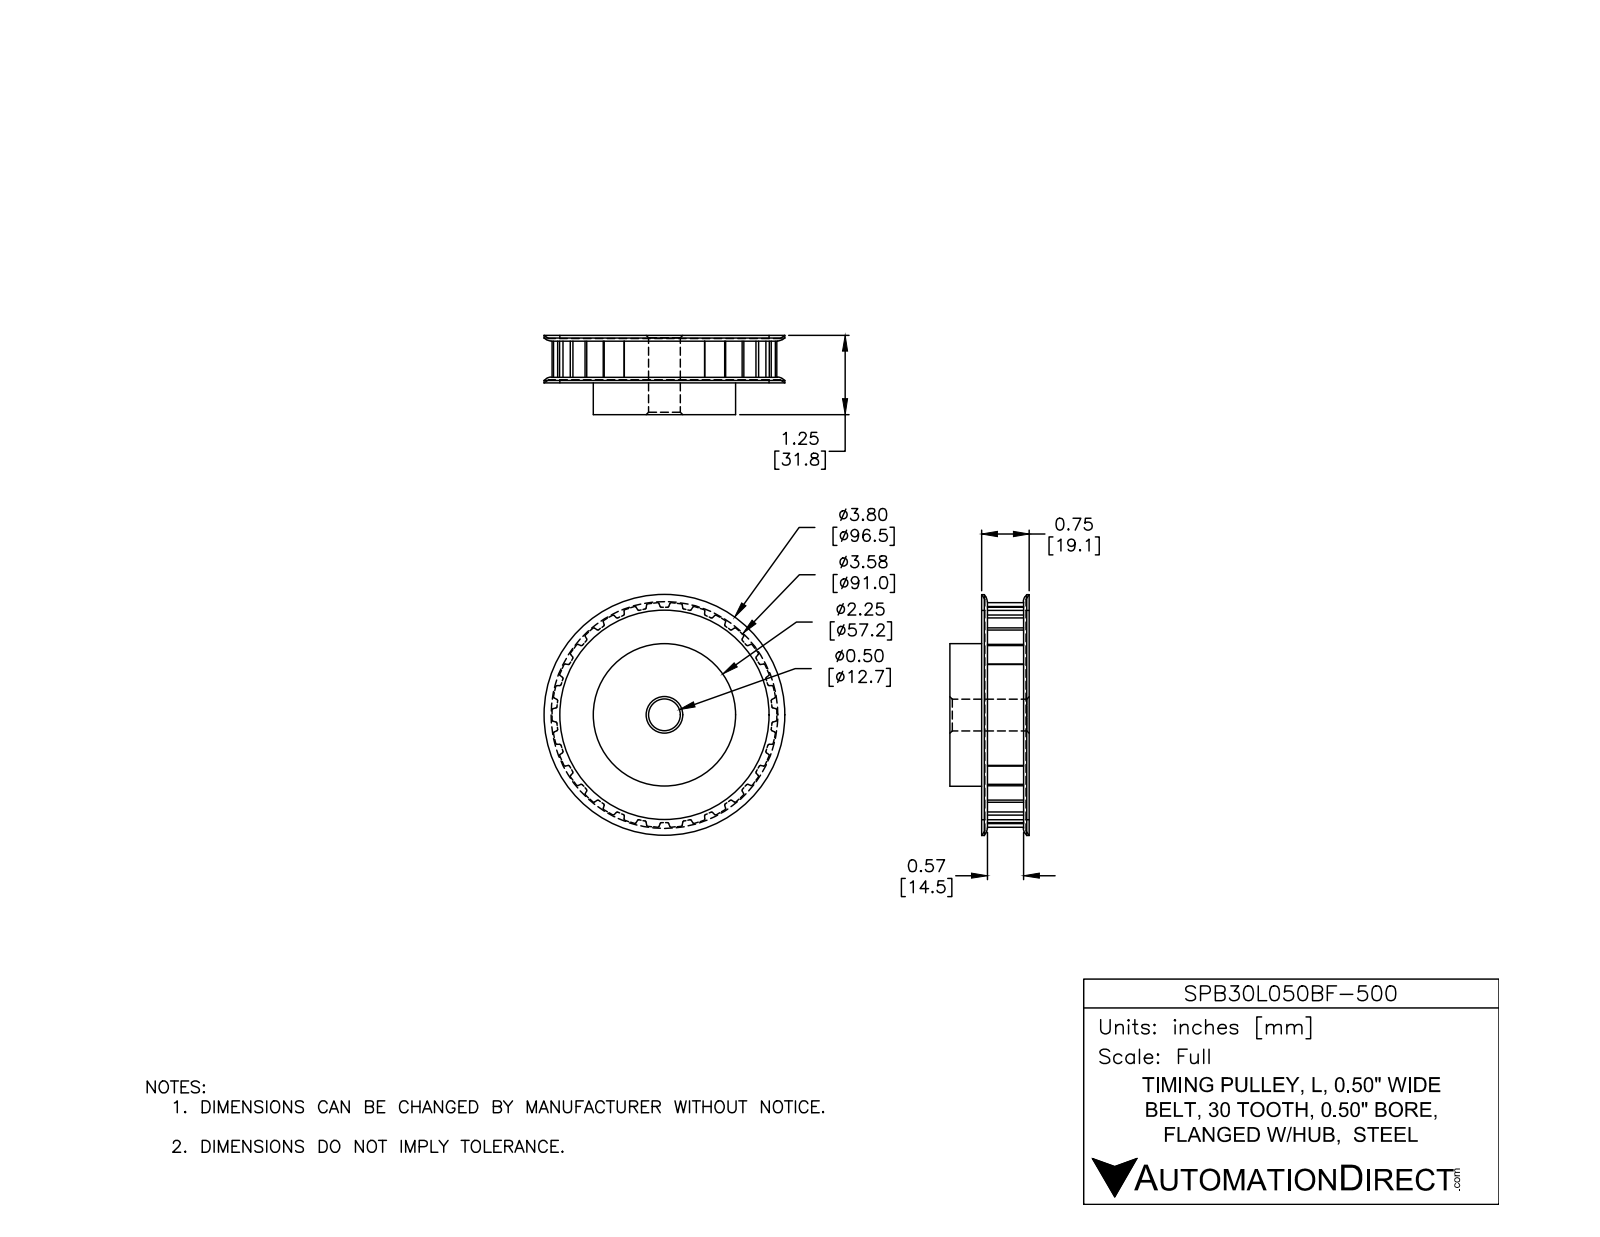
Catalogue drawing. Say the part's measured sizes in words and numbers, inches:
The part is named "SPB30L050BF-500". Its 3-D file was written by "SolidWorks 2015 (AUTOMOTIVE_DESIGN)". It is 1 solid with 300 faces: 97 planar, 187 cylindrical and 16 other. Overall it measures 3.8 by 3.8 by 1.25 inches. Its volume is 8.951 cubic inches and its surface area 41.8 square inches. Round holes: 1 of diameter 0.5. Round bosses or shafts: 1 of diameter 3.8, 1 of diameter 3.306, 1 of diameter 2.25. Partial cylindrical surfaces (rounded edges, fillets, slot ends): 120 of radius 0.02, 1 of radius 1.776. The main face-to-face distances are 0.75, 0.05, 0.7, 1.25, 0.5, 0.55, 0.65, 1.2, 0.09, 0.66.
